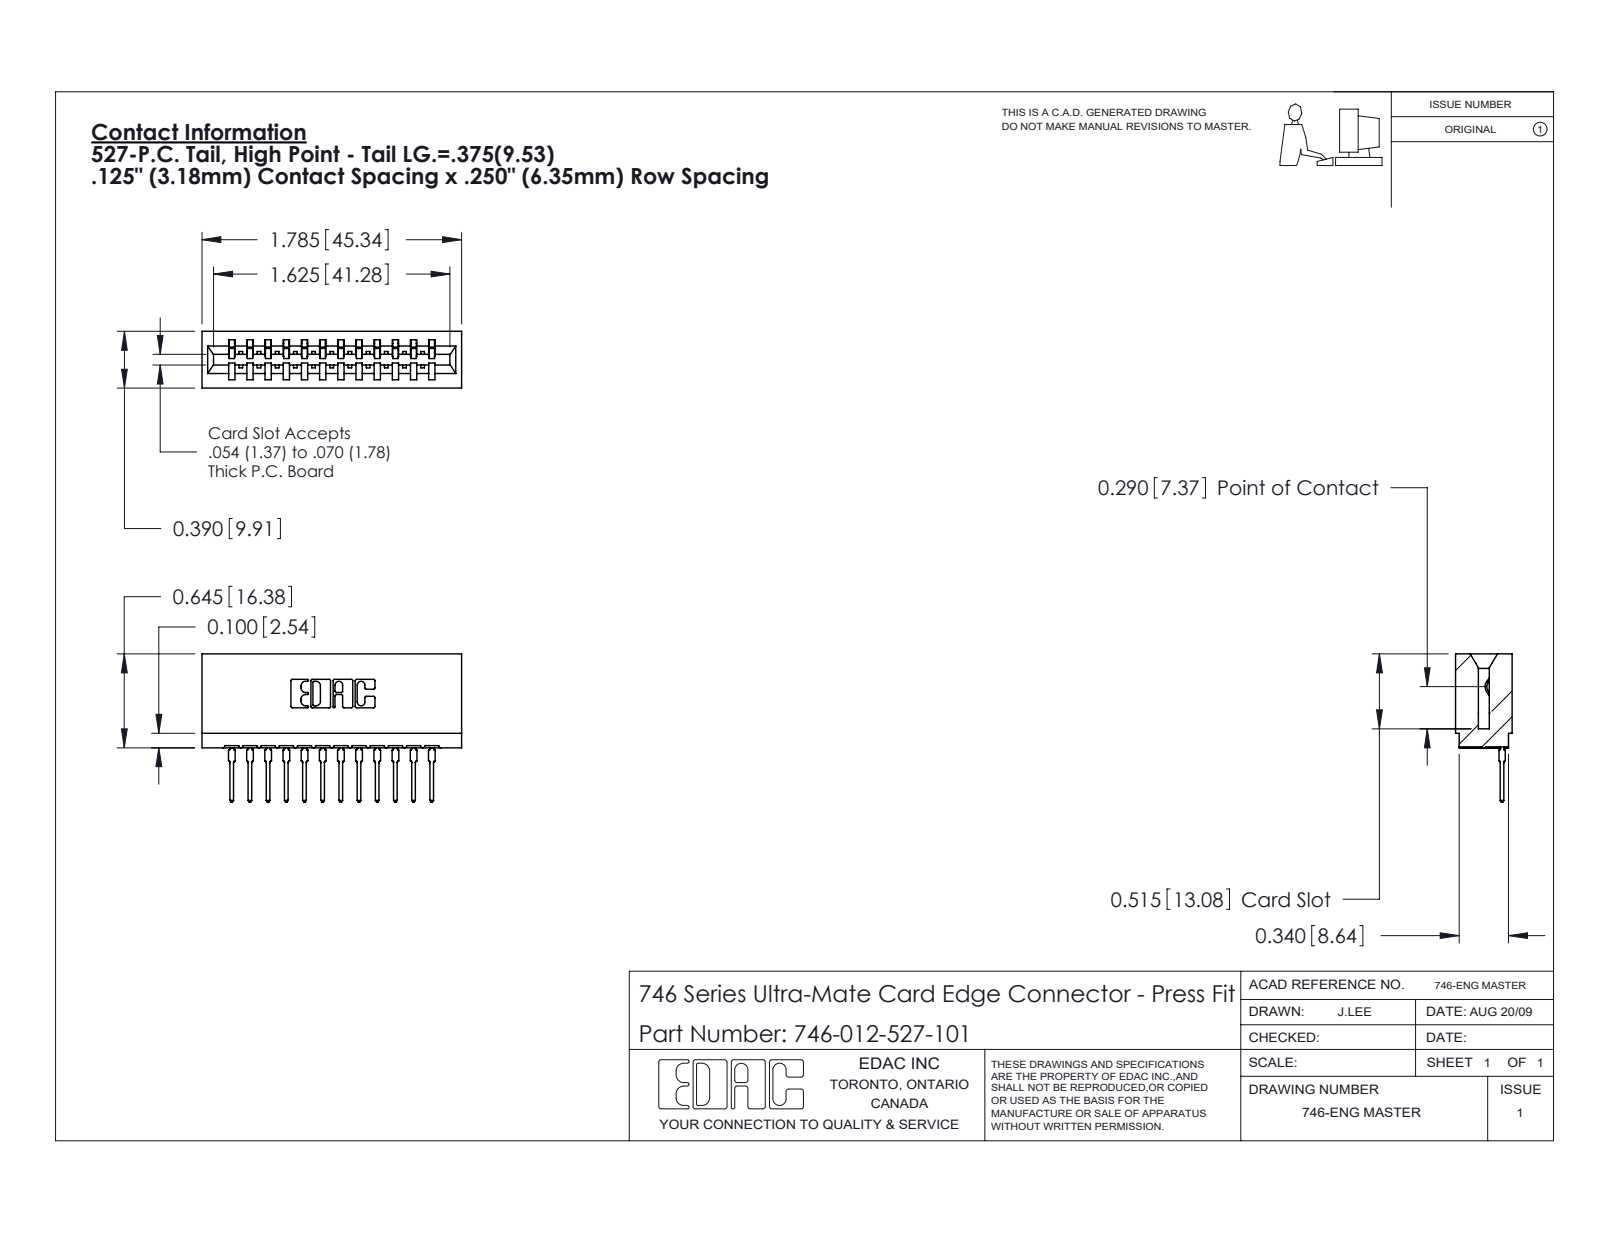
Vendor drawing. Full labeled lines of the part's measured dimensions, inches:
Part name (STEP PRODUCT): 746 Part_.515 Slot Depth - 01; 746-012-527-101; 746-292-001_527
STEP written by: SolidWorks 2020 (CONFIG_CONTROL_DESIGN)
Units: inches
Bodies: 13 solids, 1393 faces (811 planar, 270 cylindrical, 312 other)
Overall size (bounding box): 1.785 × 1.019 × 0.39
Volume: 0.302 in³ · Surface area: 10.71 in²
Partial cylindrical surfaces — rounded edges, fillets, slot ends (radius × count): R0.021 ×24, R0.01 ×22, R0.015 ×13, R0.007 ×6, R0.031 ×6, R0.005 ×4, R0.011 ×4, R0.026 ×3
Main face-to-face distances: 0.25, 0.333, 0.5, 0.057, 0.125, 0.125, 0.39, 0.042, 0.208, 0.292
